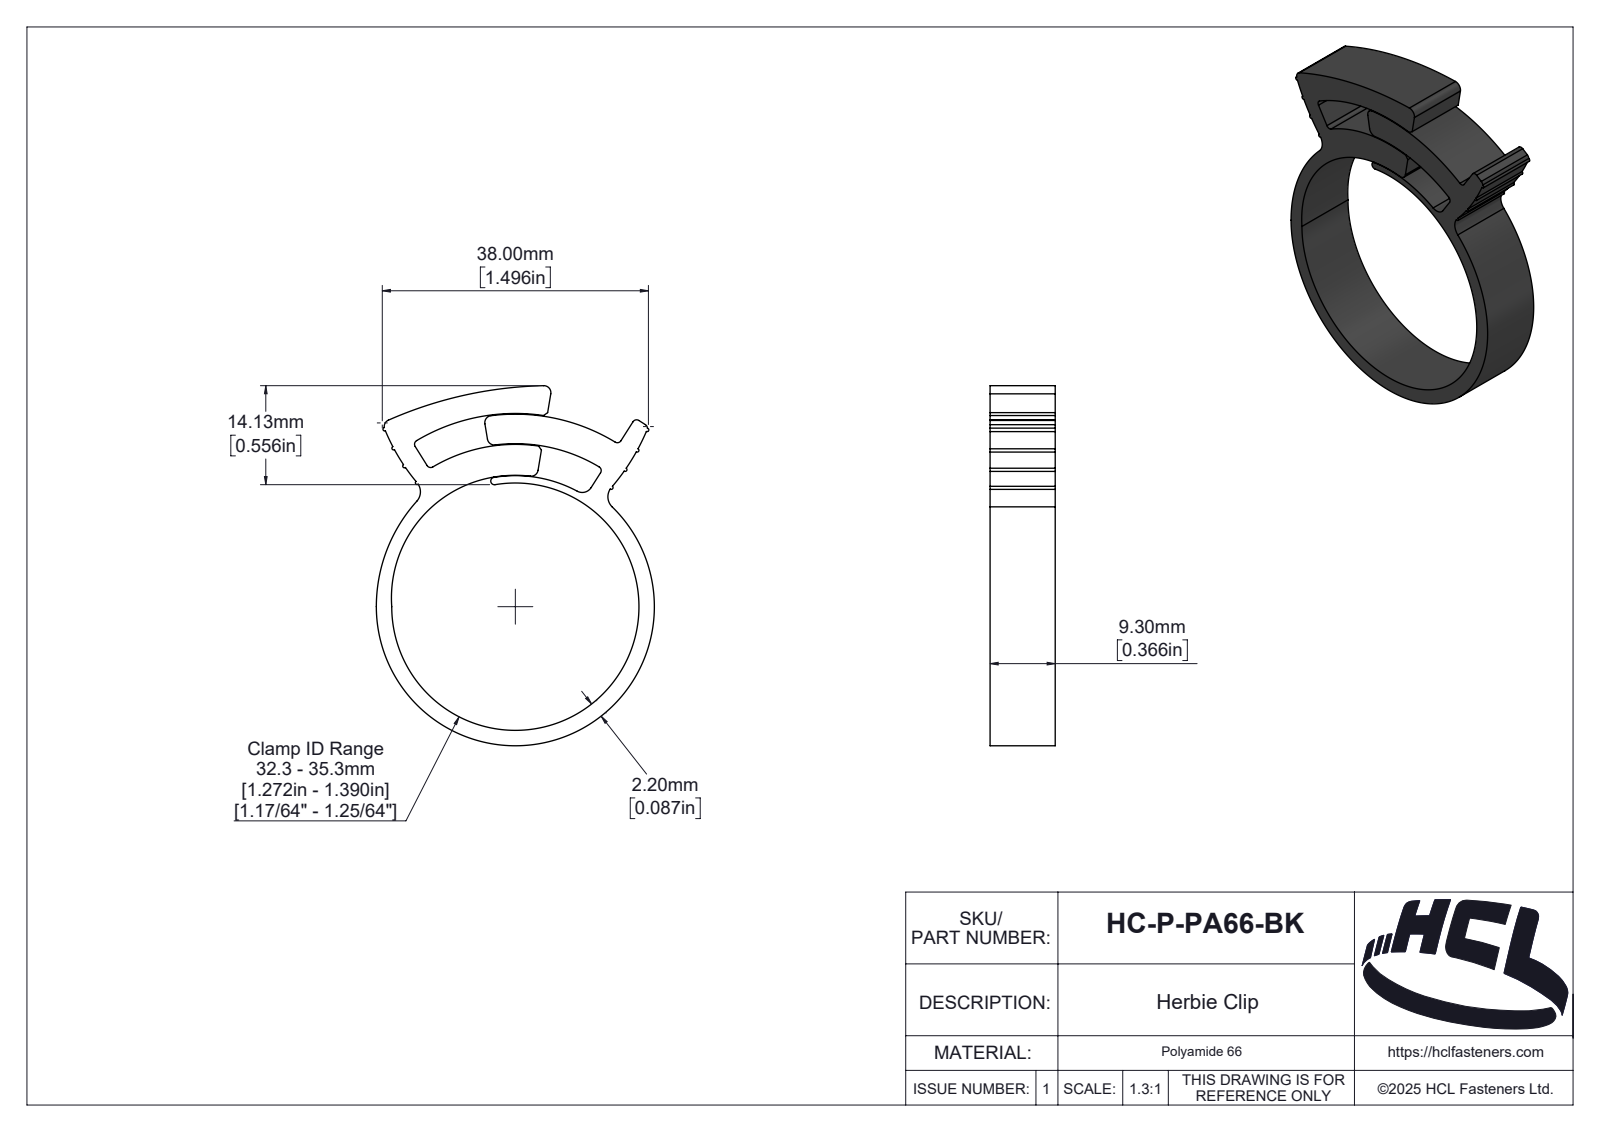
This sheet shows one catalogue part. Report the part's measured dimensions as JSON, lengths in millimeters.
{"part_name": "HC-P-PA66-BK", "step_written_by": "SolidWorks 2025 (AUTOMOTIVE_DESIGN)", "units": "millimeters", "bodies": {"solids": 1, "faces": 162, "planar": 13, "cylindrical": 100, "other": 49}, "overall_size": [51.39, 39.7, 9.3], "volume_mm3": 4768, "surface_area_mm2": 4555, "partial_cylinders_radius": [[0.25, 8], [0.6, 6], [1, 5], [2, 2], [0.17, 1], [0.53, 1], [0.67, 1], [0.84, 1]], "face_to_face_distances": [9.3]}
